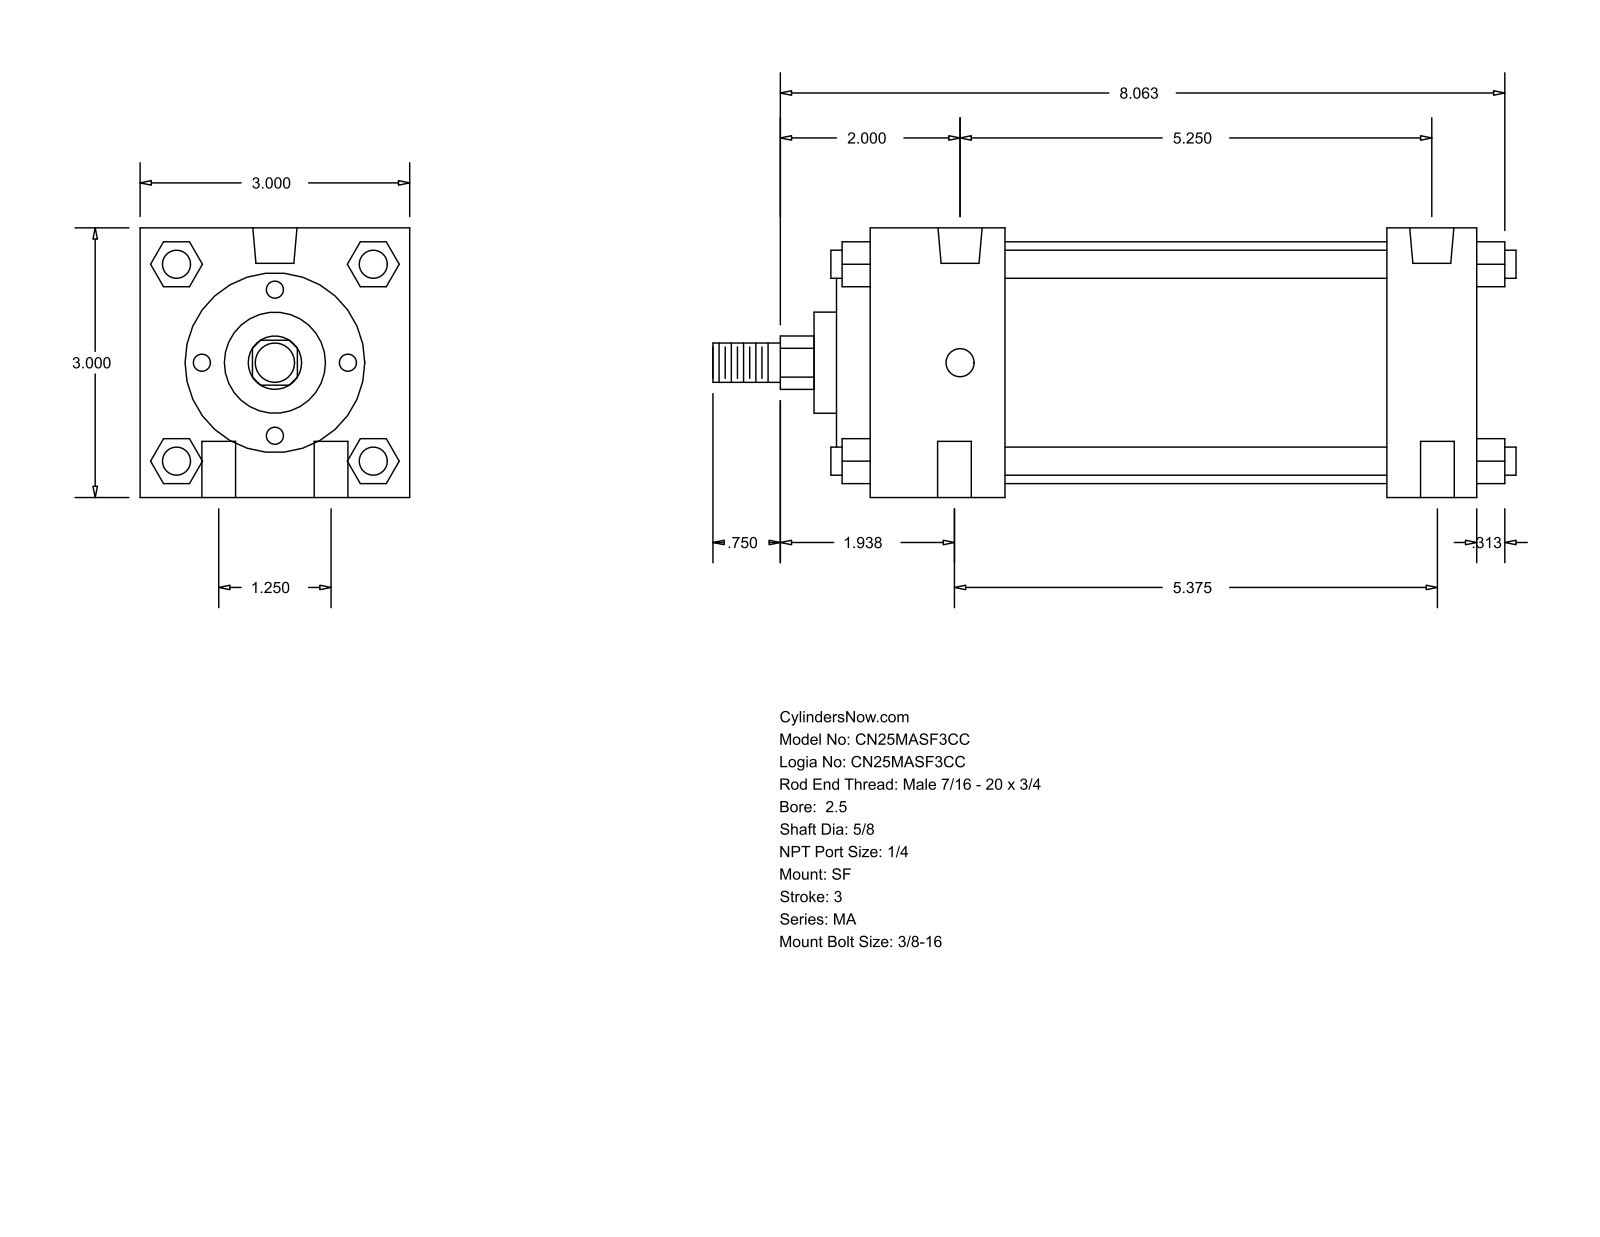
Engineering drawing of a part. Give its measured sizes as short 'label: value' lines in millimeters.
name: MA_SF__0250_0.625
written by: GSSL Pune (CONFIG_CONTROL_DESIGN)
unit: mm
bodies: 0 solids, 126 faces (95 planar, 31 cylindrical, 0 other)
size: 227.01 × 76.2 × 76.2
holes: 4× ⌀9.53, 2× ⌀7.94, 2× ⌀12.49
bosses: 4× ⌀7.94, 1× ⌀68.33, 1× ⌀50.8, 1× ⌀28.57, 1× ⌀15.88, 1× ⌀11.11
rounds: 1× R7.54
face distances: 76.2, 171.45, 25.4, 146.05, 38.1, 107.95, 133.35, 12.7, 9.52, 47.62
hole spacings: 15.96, 135.87, 31.76, 133.35, 136.53, 140.18
